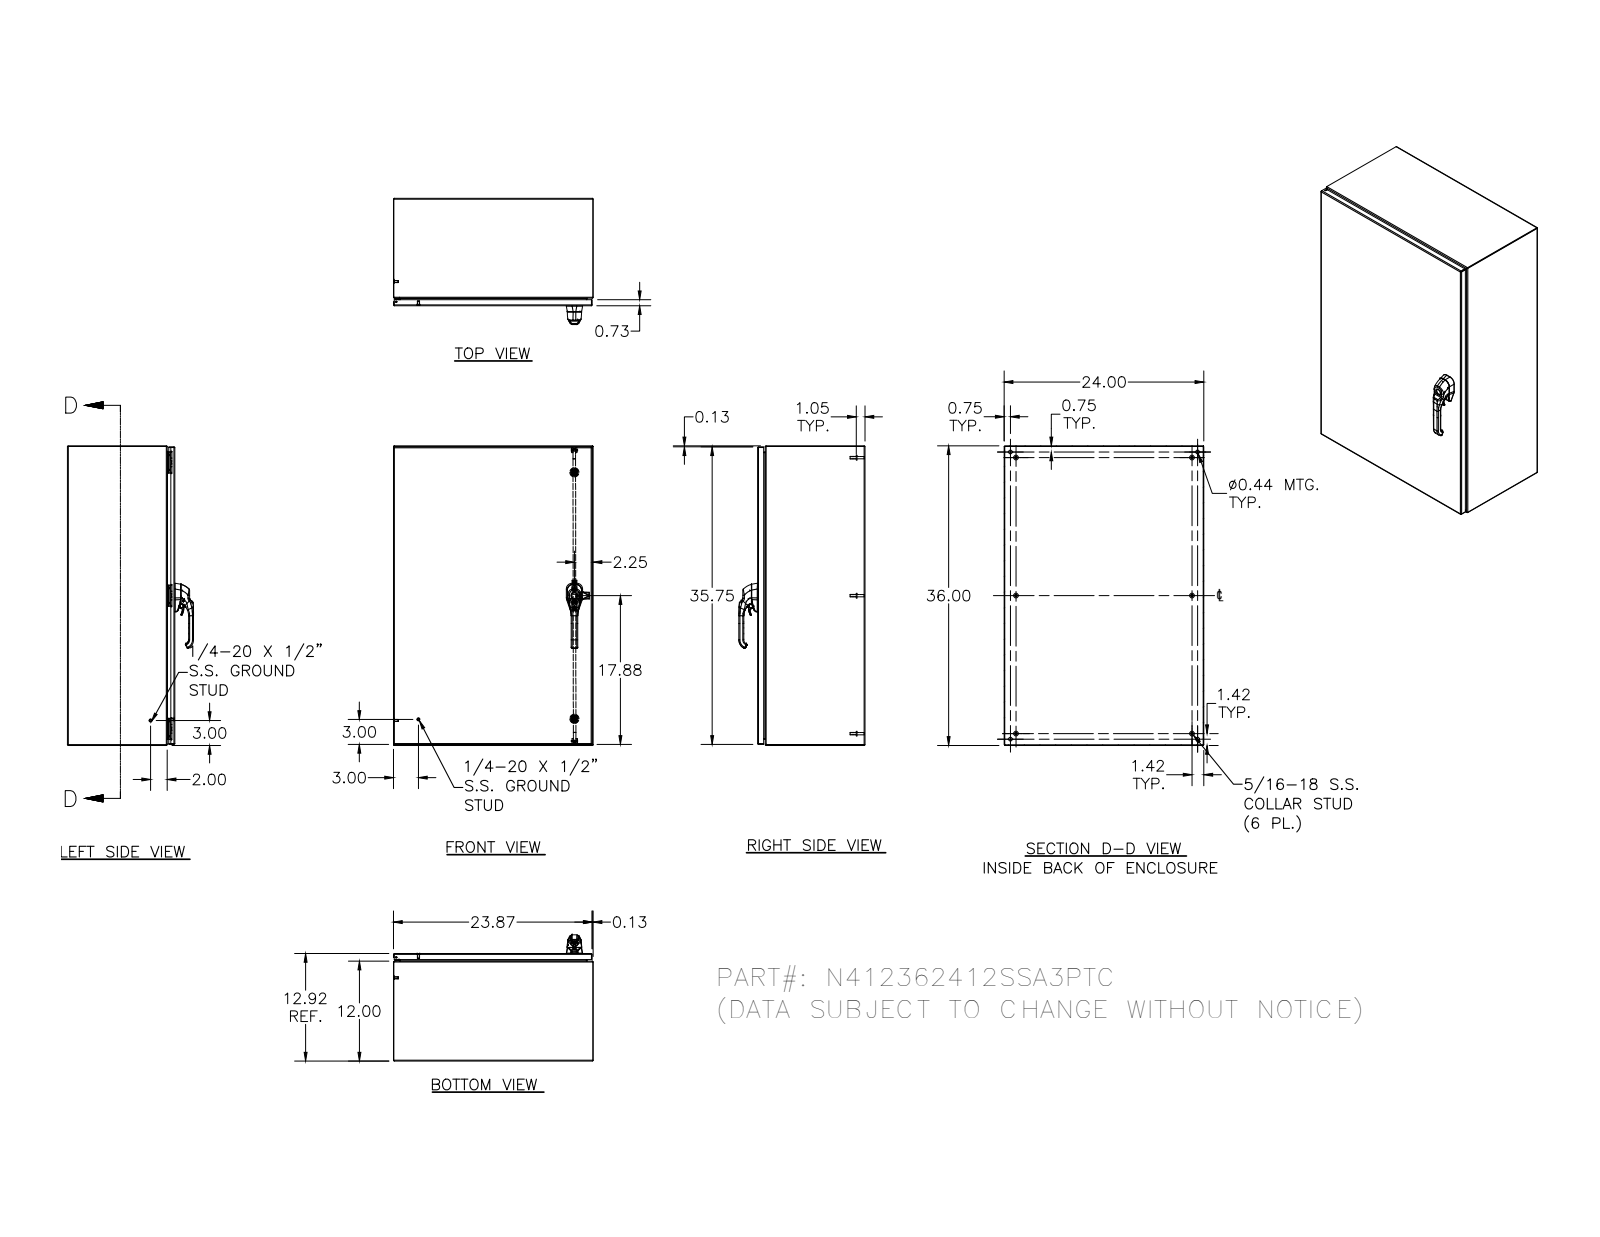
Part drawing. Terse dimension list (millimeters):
name: N412362412SSA3PTC; N412362412SSA3PTCBKP; N4123624SSA3PTCLID; HFW328176 (+8 more)
written by: Autodesk Inventor 2011 (AUTOMOTIVE_DESIGN)
unit: mm
bodies: 74 solids, 3524 faces (1171 planar, 1297 cylindrical, 1056 other)
size: 914.4 × 609.6 × 385.2
volume: 4 325 000 mm³; area: 4 521 000 mm²
holes: 7× ⌀4.8, 6× ⌀2.4, 6× ⌀3.9, 6× ⌀4.2, 6× ⌀4.4, 5× ⌀4.2, 4× ⌀5, 4× ⌀11.1, 3× ⌀4, 3× ⌀5.4, 2× ⌀2.7, 2× ⌀4.1
bosses: 14× ⌀6.4, 6× ⌀14.3, 6× ⌀9.1, 6× ⌀8.1, 6× ⌀7.6, 6× ⌀7, 6× ⌀6.5, 6× ⌀6
rounds: 178× R0.5, 101× R0.3, 38× R1.3, 34× R0.8, 26× R0.4, 23× R3, 21× R0.5, 21× R3.2
face distances: 1.9, 326.2, 607.7, 324.3, 328.1, 912.5, 605.8, 609.6, 914.4, 910.6
hole spacings: 406.4, 406.3, 812.7, 406.6, 0.4, 16.8, 423.1, 580.9
